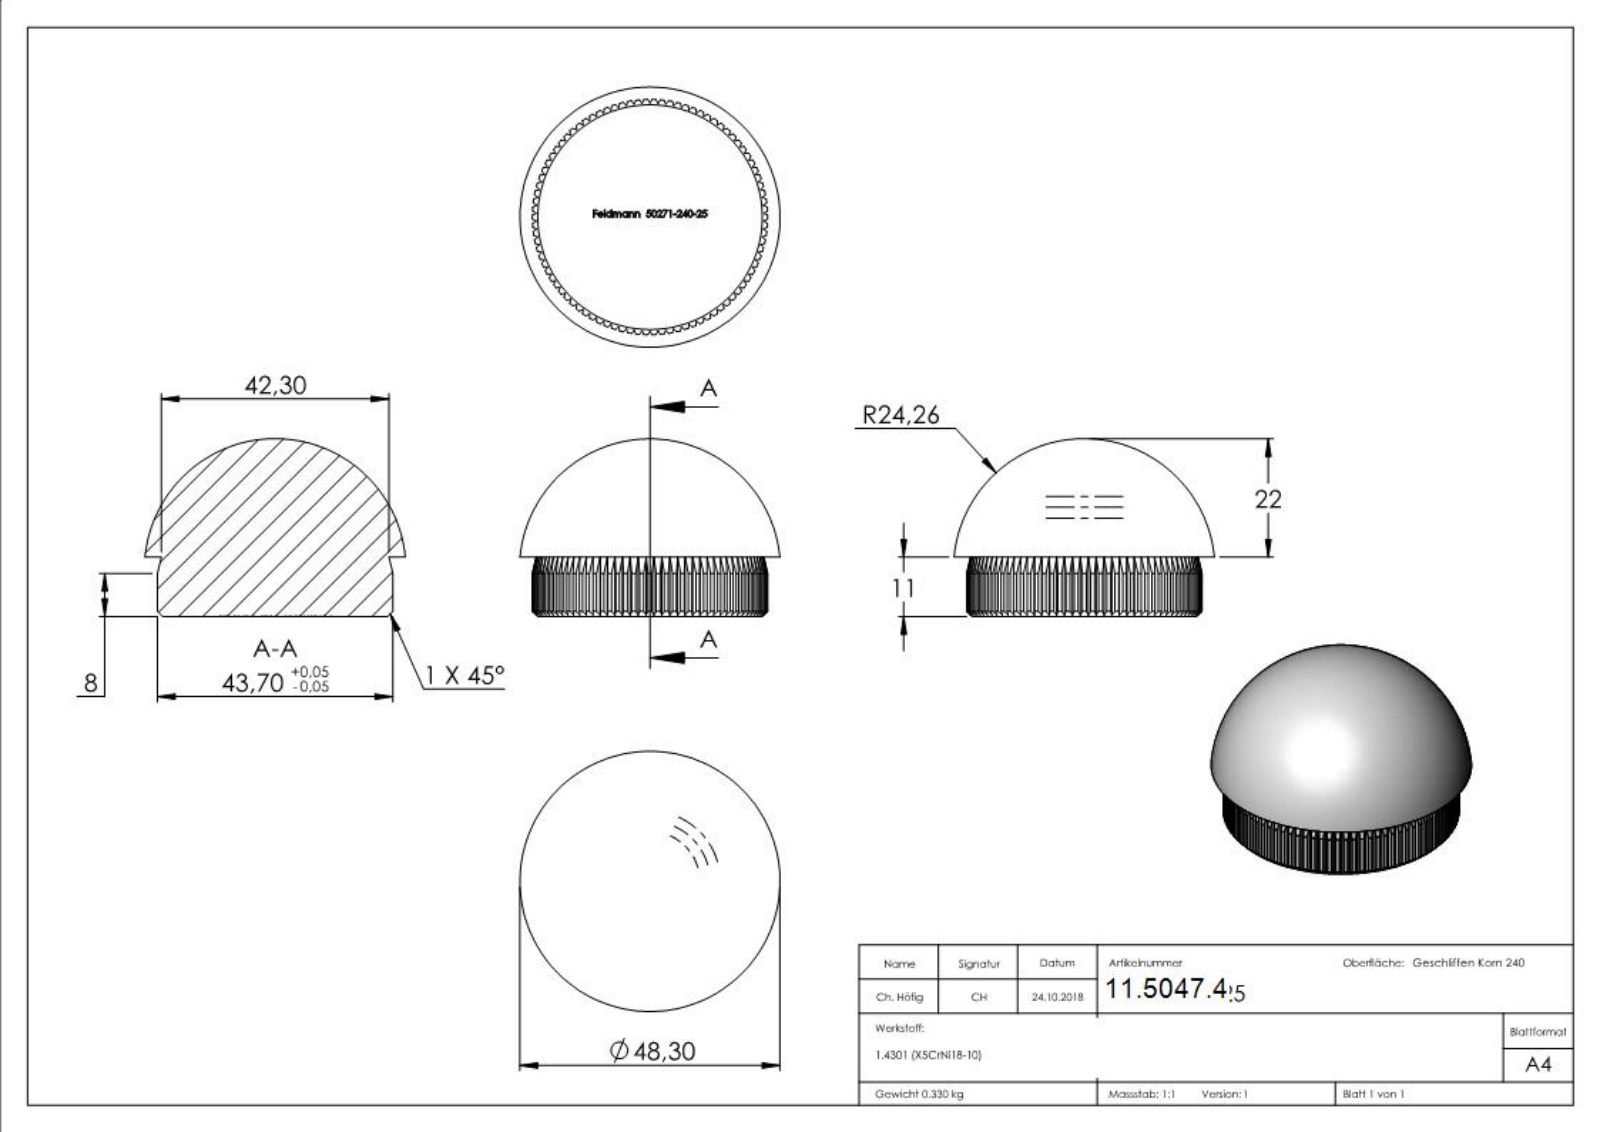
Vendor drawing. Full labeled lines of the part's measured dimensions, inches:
Part name (STEP PRODUCT): 50271-240-25
STEP written by: SolidWorks 2015 (CONFIG_CONTROL_DESIGN)
Units: inches
Bodies: 1 solid, 584 faces (306 planar, 90 cylindrical, 188 other)
Overall size (bounding box): 1.902 × 1.902 × 1.299
Volume: 2.551 in³ · Surface area: 11.39 in²
Partial cylindrical surfaces — rounded edges, fillets, slot ends (radius × count): R0.86 ×1
Main face-to-face distances: 0.433, 0.833, 0.832, 0.833, 0.834, 0.831, 0.429, 0.417, 0.416, 0.052
